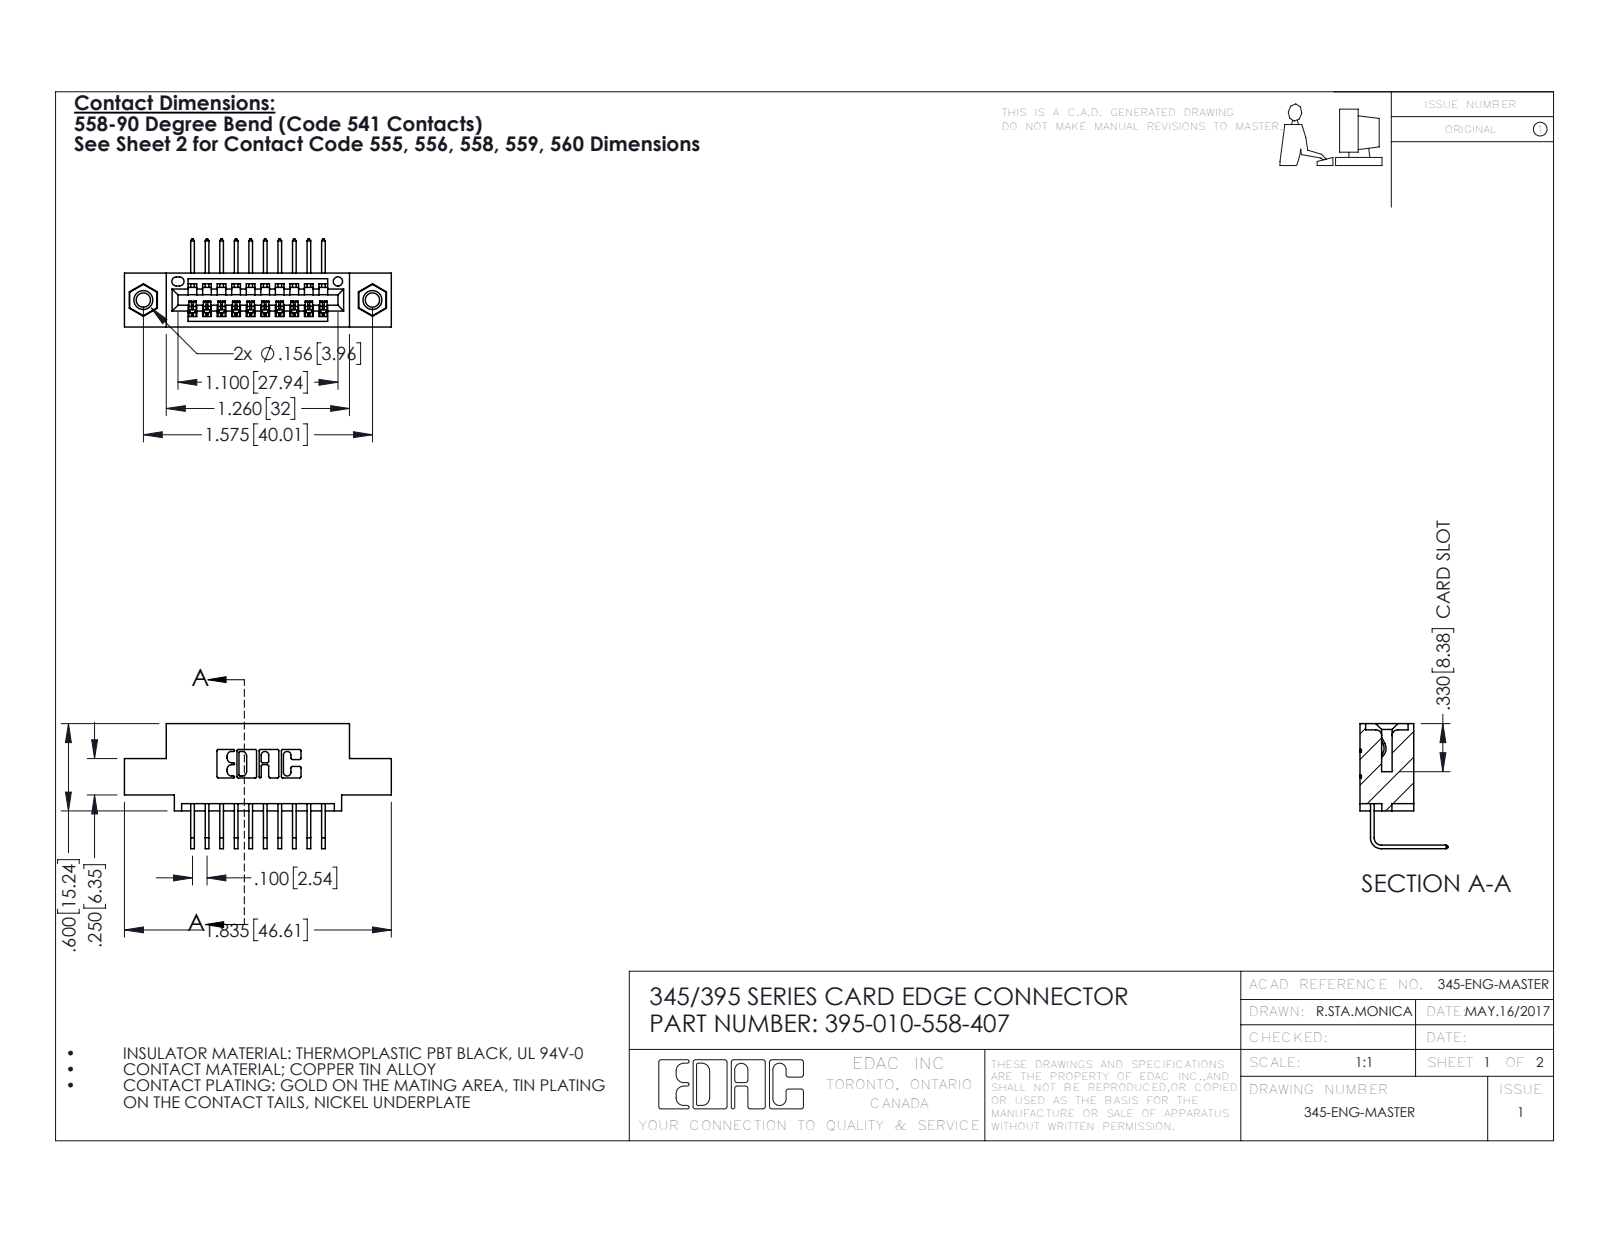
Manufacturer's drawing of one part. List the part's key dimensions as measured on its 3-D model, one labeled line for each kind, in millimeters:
Part name (STEP PRODUCT): 345-292-001_558 Tail - 2; 345 Part_0.110 Offset - 0.156 Dia-TI; 395-010-558-407; 345-250-001_345-250-005-103
STEP written by: SolidWorks 2016 (CONFIG_CONTROL_DESIGN)
Units: millimetres
Bodies: 13 solids, 790 faces (536 planar, 238 cylindrical, 16 other)
Overall size (bounding box): 46.6 × 21.8 × 15.4
Volume: 4 110 mm³ · Surface area: 5 339 mm²
Round holes (diameter × count): ⌀2.5 ×2, ⌀3.2 ×2, ⌀4 ×2, ⌀1.6 ×1
Round bosses / shafts (diameter × count): ⌀3.9 ×2
Partial cylindrical surfaces — rounded edges, fillets, slot ends (radius × count): R0.3 ×22, R0.2 ×20, R0.2 ×6, R0.8 ×6, R0.7 ×3, R0.8 ×2, R1 ×2, R0.4 ×1
Main face-to-face distances: 5.1, 1.8, 7.6, 9.4, 2.5, 2.5, 6.9, 0.6, 15.2, 1.5
Hole centre spacings: 6.9, 34.1, 40
